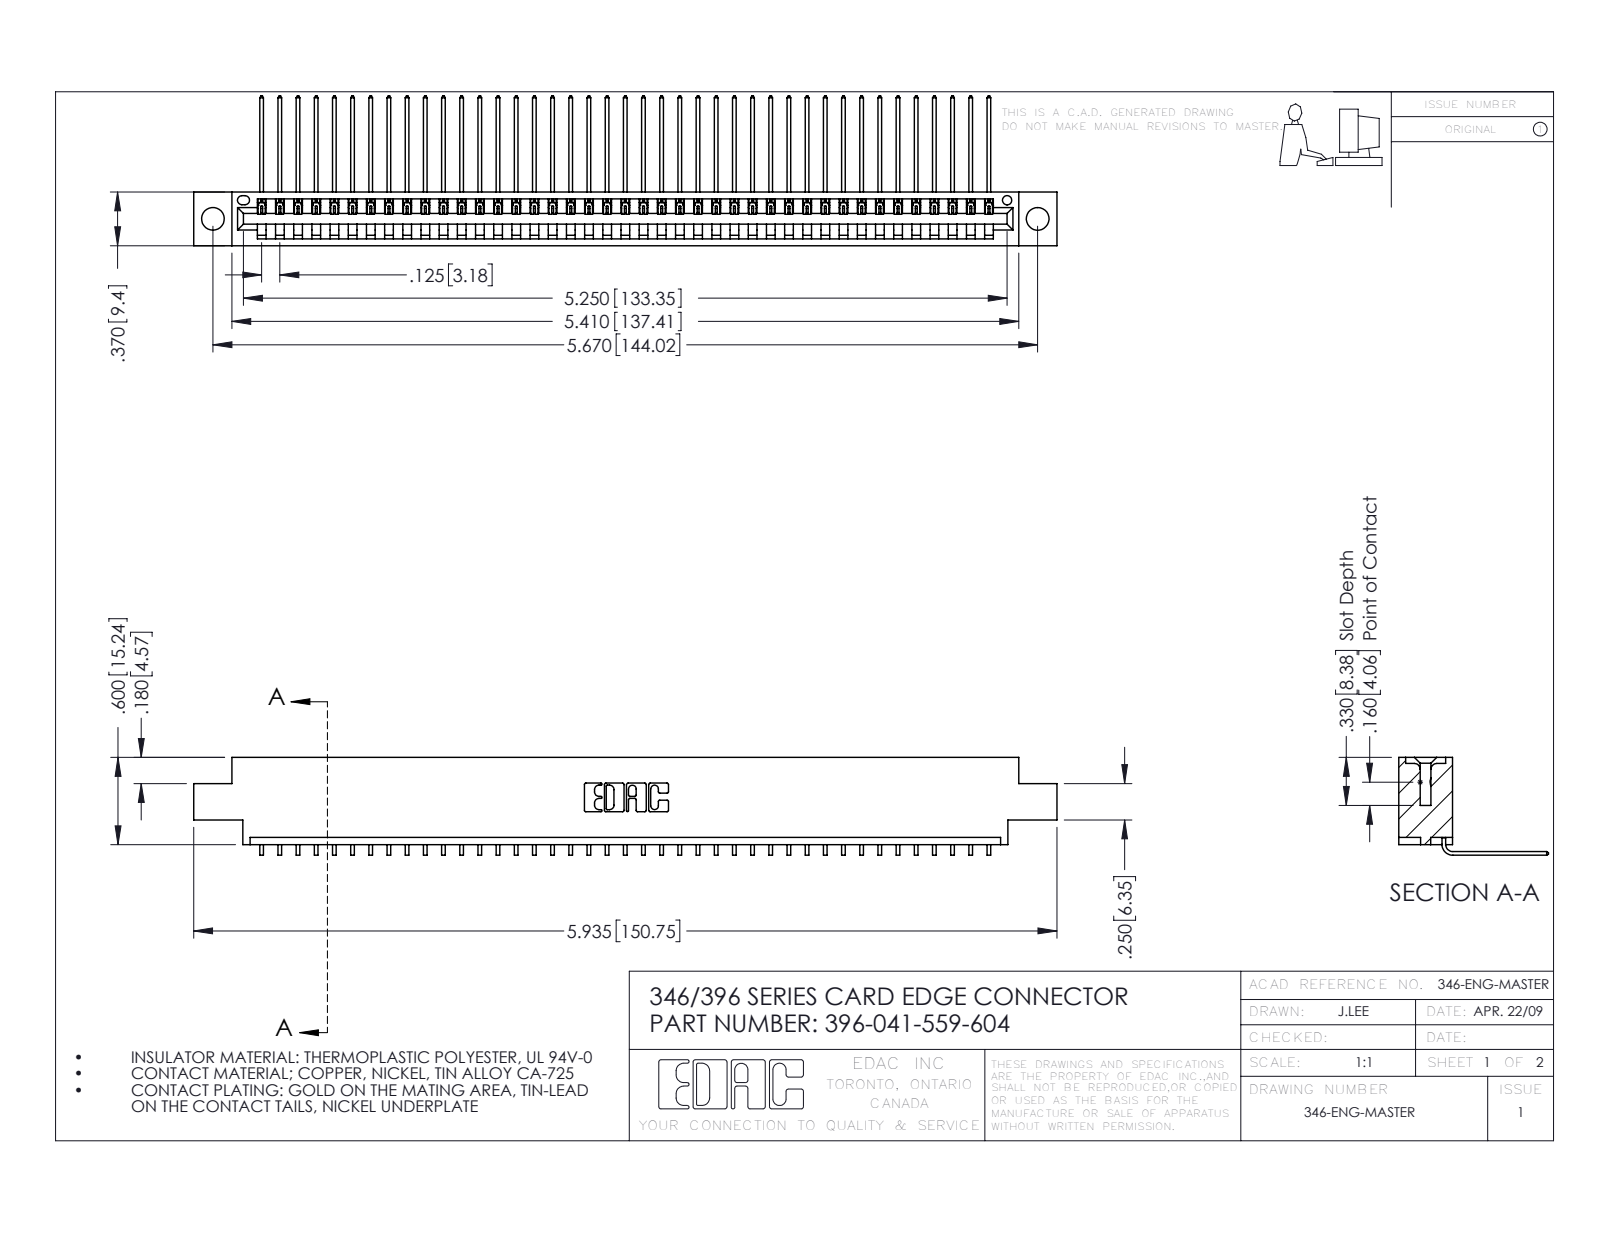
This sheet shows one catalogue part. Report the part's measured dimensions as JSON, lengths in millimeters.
{"part_name": "396-041-559-604; 345-292-001_558 559 Tail - 1; 346 Part_0.170 Offset - 0.156 Dia-TH", "step_written_by": "SolidWorks 2016 (CONFIG_CONTROL_DESIGN)", "units": "millimeters", "bodies": {"solids": 42, "faces": 2586, "planar": 1802, "cylindrical": 784, "other": 0}, "overall_size": [150.7, 26.2, 17.1], "volume_mm3": 14300, "surface_area_mm2": 18660, "round_holes": [[4, 2], [1.6, 1]], "partial_cylinders_radius": [[0.2, 82], [0.3, 22], [0.2, 6], [0.8, 6], [0.7, 3], [0.8, 2], [1, 2], [0.4, 1]], "face_to_face_distances": [1.2, 8.2, 9.4, 0.6, 6.4, 1.8, 7.6, 3.8, 5.6, 2.5], "hole_center_spacings": [6.2, 138.7, 144]}
